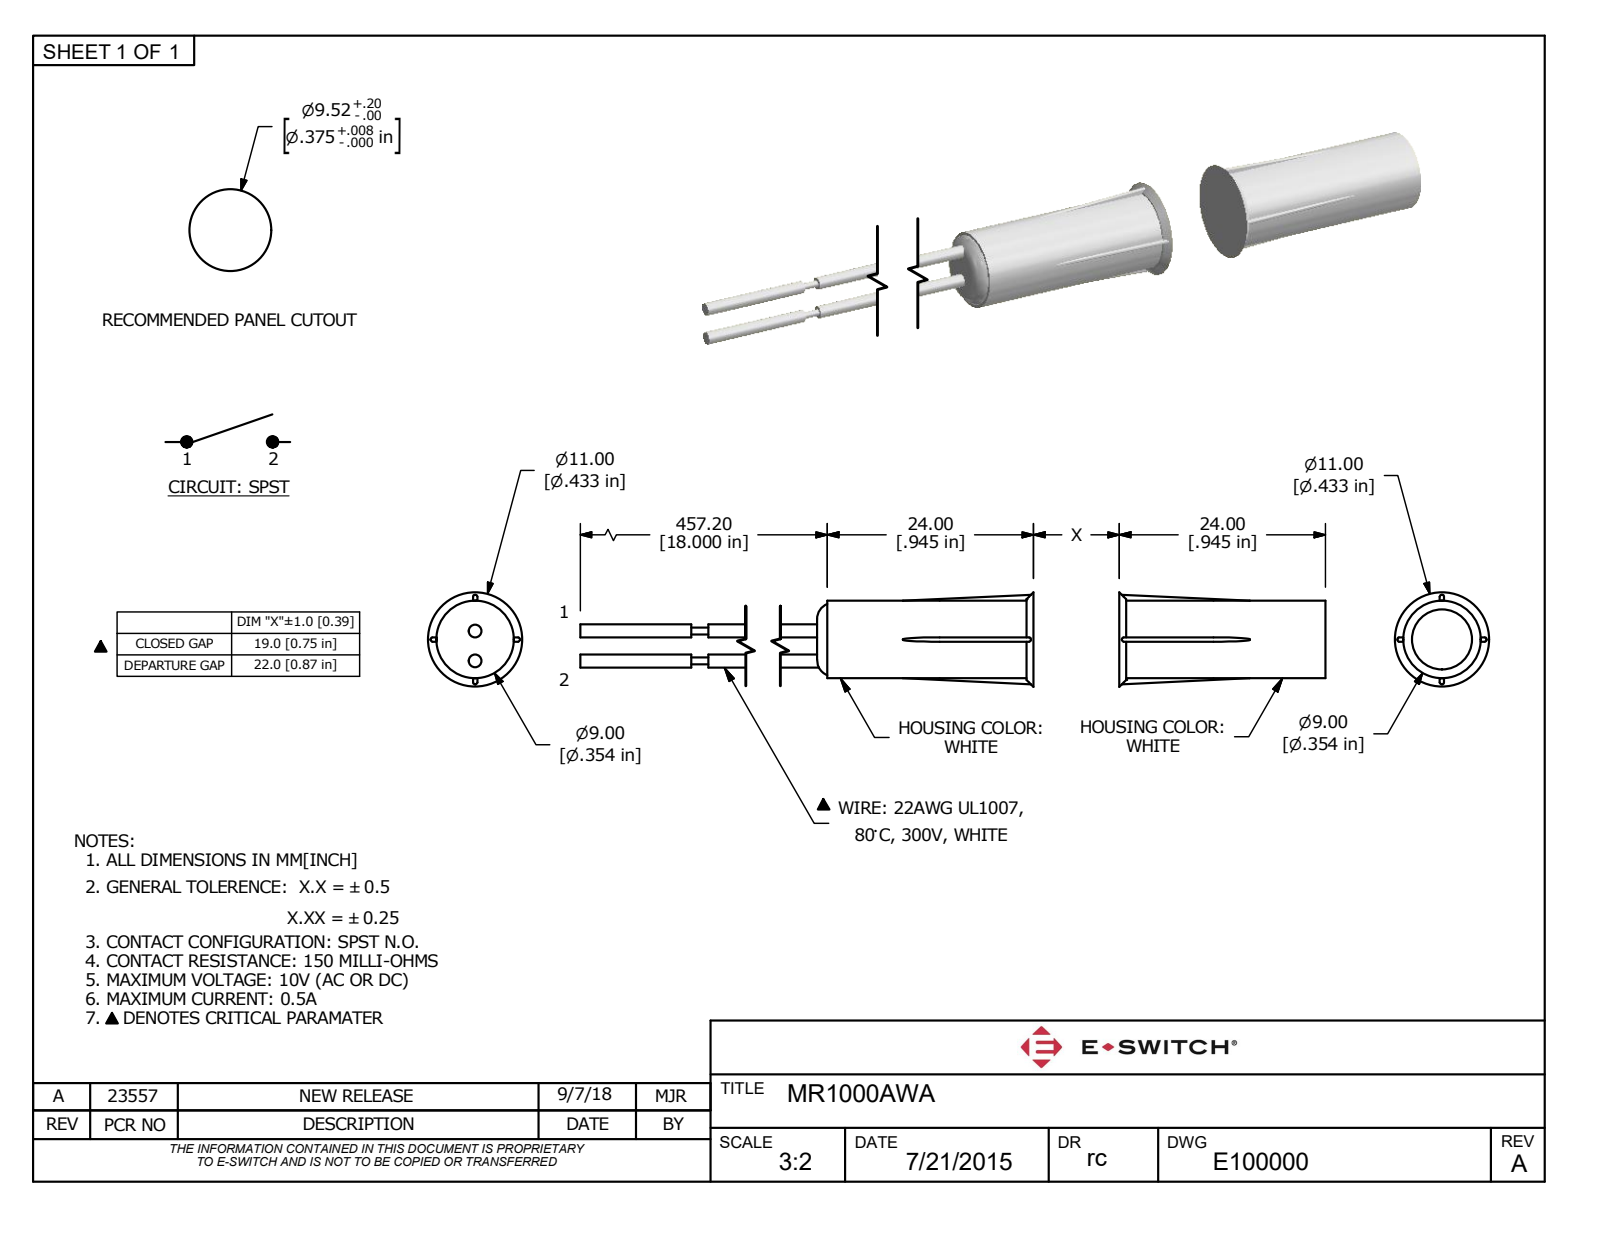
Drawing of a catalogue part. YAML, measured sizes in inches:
part_name: "MR1000AWA"
step_written_by: "Autodesk Inventor 2018 (AP242_MANAGED_MODEL_BASED_3D_ENGINEERING_MIM_LF)"
units: inches
bodies: {solids: 2, faces: 122, planar: 91, cylindrical: 27, other: 4}
overall_size: [20.638, 0.433, 0.433]
volume: 0.283
surface_area: 9.684
round_holes:
  - {diameter: 0.276, count: 1}
round_bosses_or_shafts:
  - {diameter: 0.059, count: 2}
  - {diameter: 0.031, count: 2}
  - {diameter: 0.354, count: 1}
partial_cylinders:
  - {radius: 0.008, count: 16}
face_to_face_distances: [0.748, 0.167, 0.187, 0.945, 1.693, 0.354, 0.02, 0.992, 1.74, 2.685]
